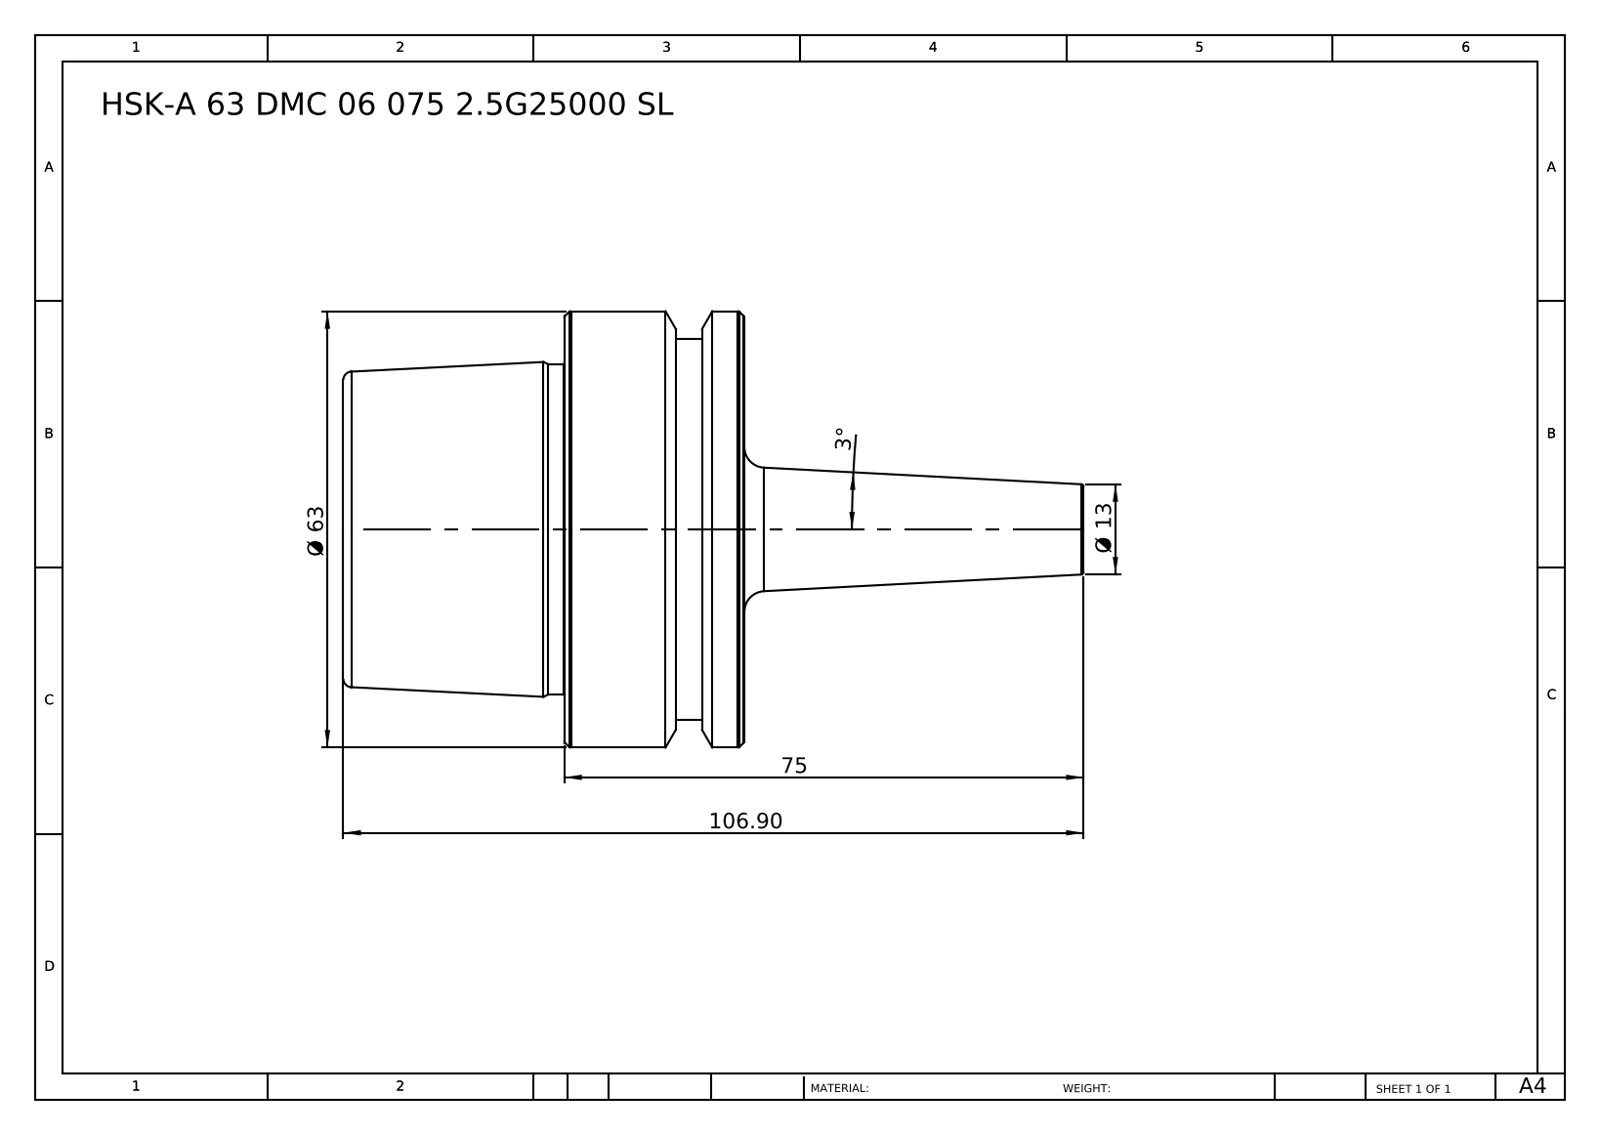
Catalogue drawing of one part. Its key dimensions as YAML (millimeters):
part_name: "HSK-A 63 DMC 06 075 2.5G25000 SL"
step_written_by: "SolidWorks 2014 (CONFIG_CONTROL_DESIGN)"
units: millimeters
bodies: {solids: 1, faces: 46, planar: 6, cylindrical: 8, other: 32}
overall_size: [106.9, 63, 63]
volume: 142086
surface_area: 18854
round_bosses_or_shafts:
  - {diameter: 63, count: 1}
  - {diameter: 55, count: 1}
  - {diameter: 47.78, count: 1}
face_to_face_distances: [57.9, 26, 31.9, 6.1, 19.9, 51.8, 9.9, 3.8, 16.1, 48]
